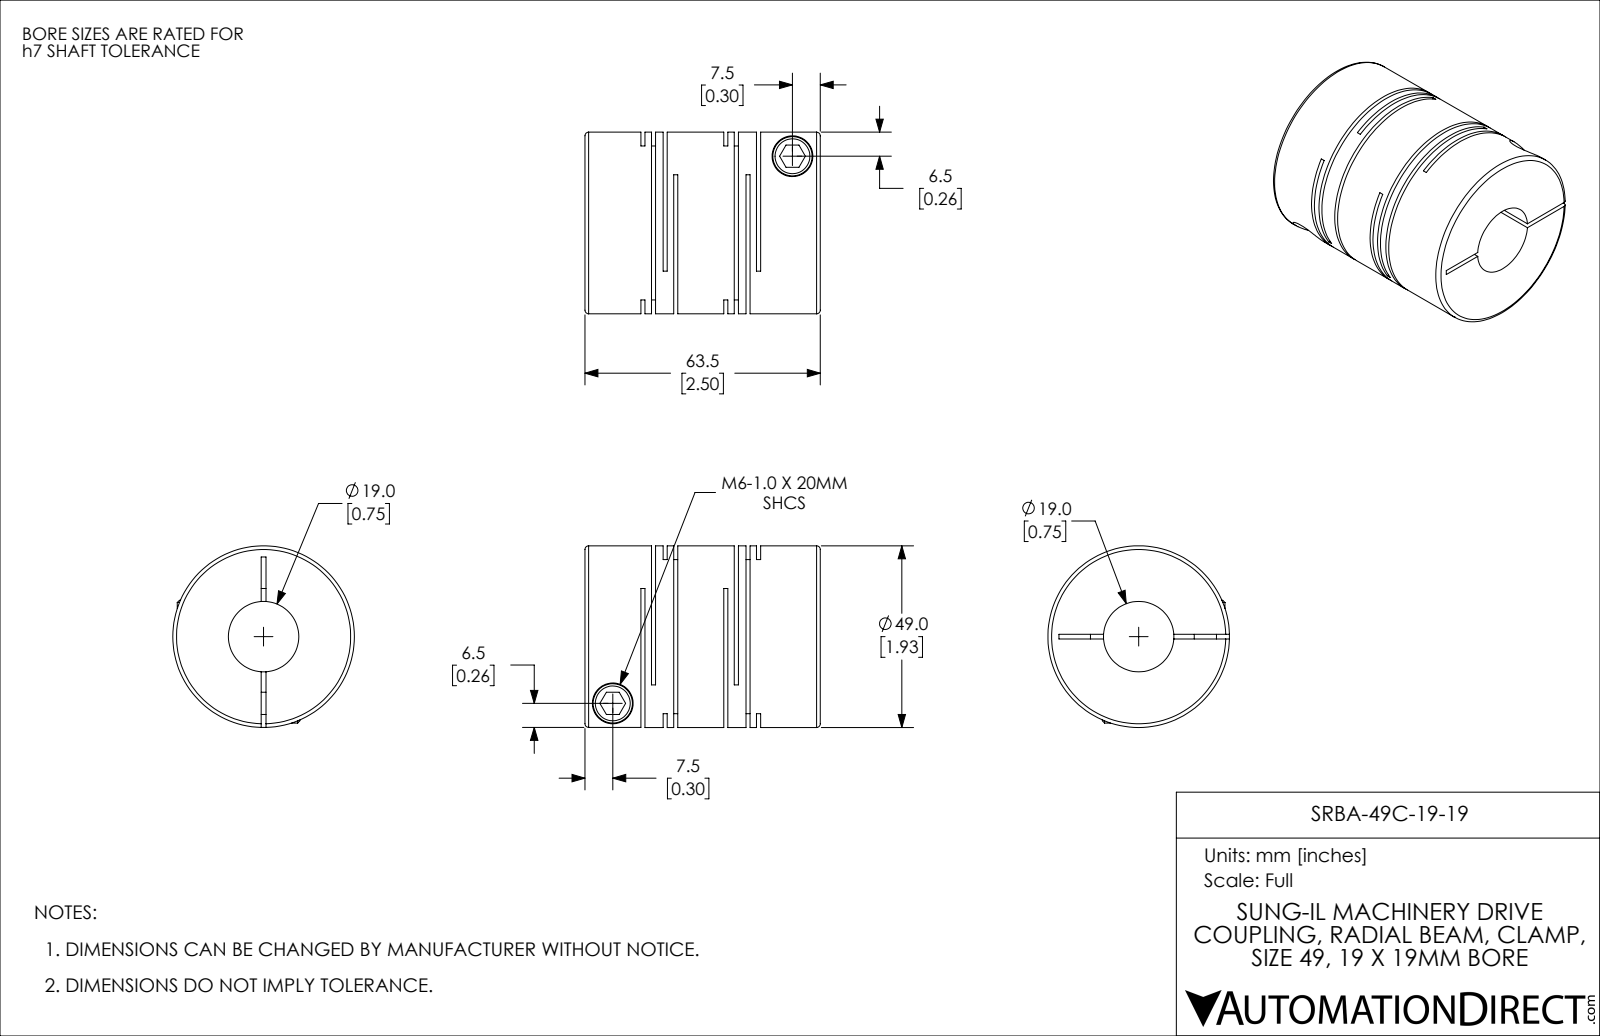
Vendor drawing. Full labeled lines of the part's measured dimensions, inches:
Part name (STEP PRODUCT): SRBA-49C-19-19
STEP written by: SolidWorks 2021 (CONFIG_CONTROL_DESIGN)
Units: inches
Bodies: 1 solid, 114 faces (60 planar, 42 cylindrical, 12 other)
Overall size (bounding box): 2.5 × 1.929 × 1.929
Volume: 5.362 in³ · Surface area: 59.53 in²
Round holes (diameter × count): ⌀0.236 ×2, ⌀0.433 ×2, ⌀0.748 ×1
Round bosses / shafts (diameter × count): ⌀0.417 ×2, ⌀1.929 ×1
Main face-to-face distances: 0.236, 0.043, 0.88, 0.112, 0.069, 0.193, 0.837, 0.124, 0.768, 0.644
